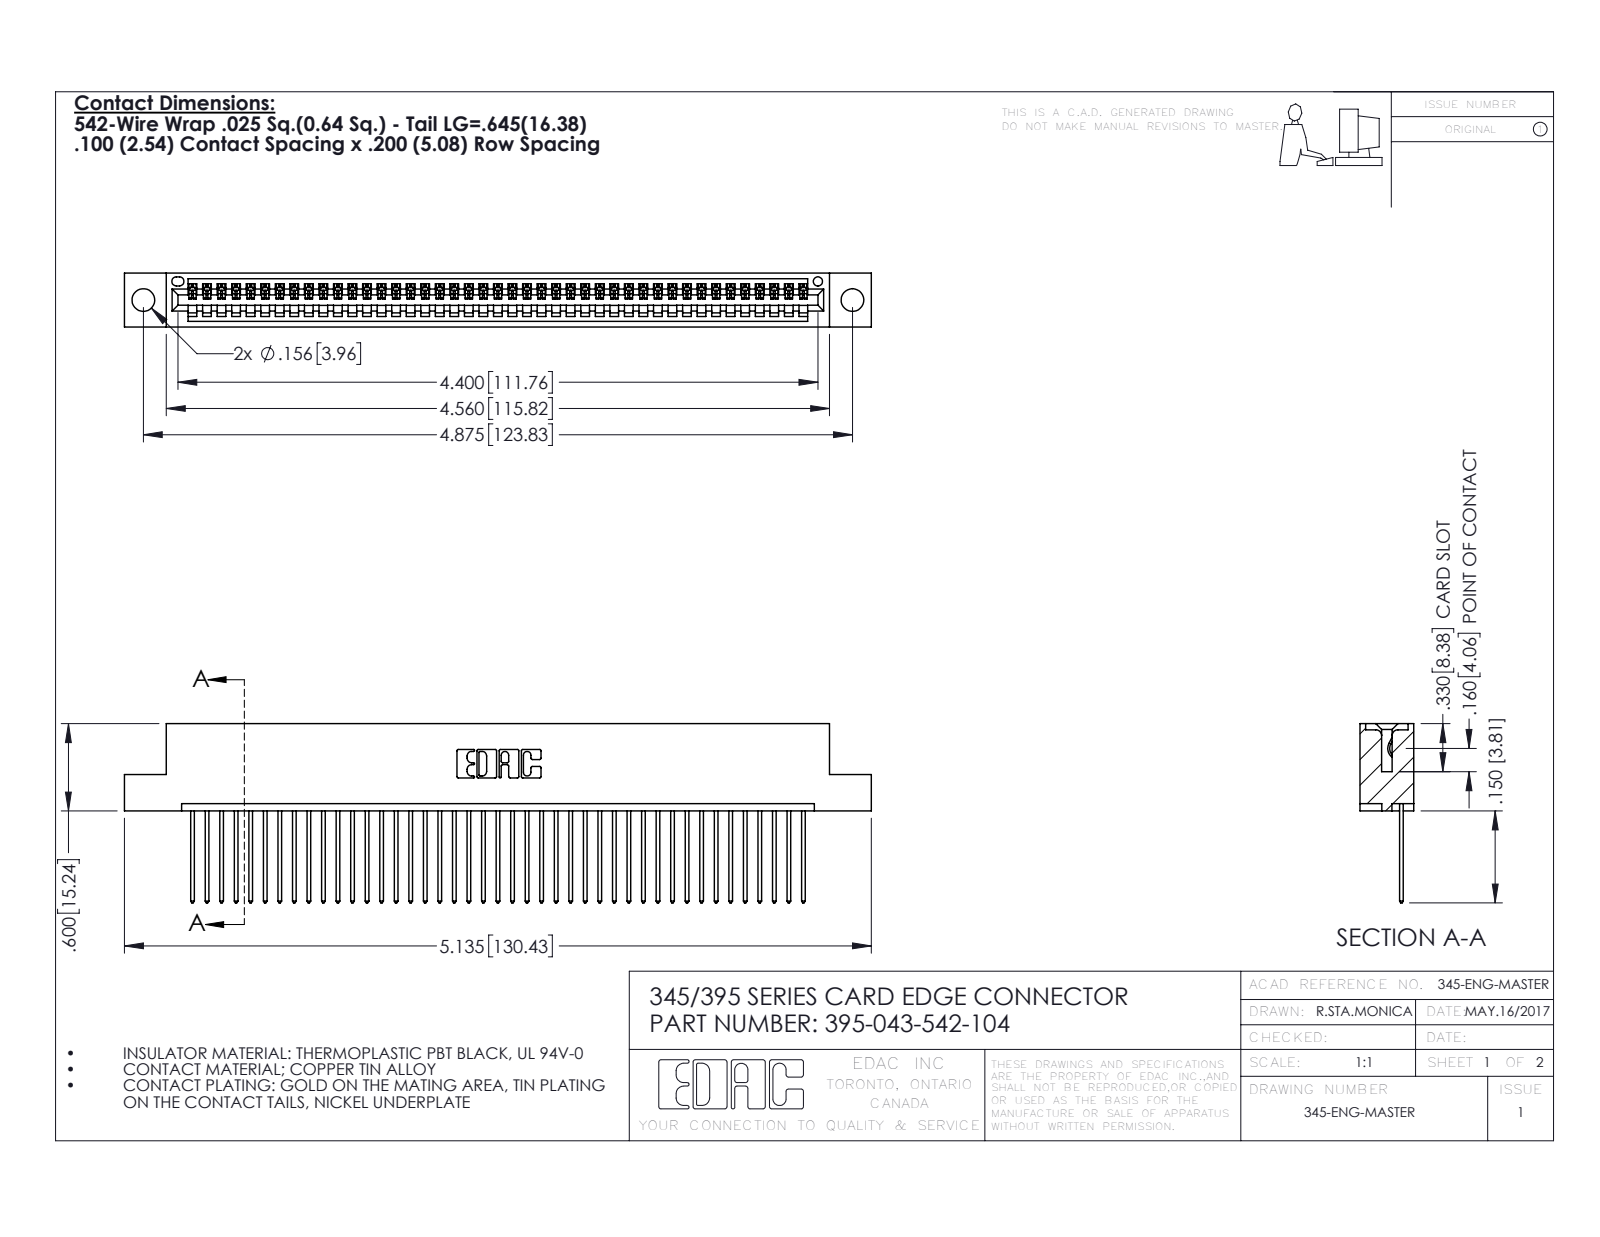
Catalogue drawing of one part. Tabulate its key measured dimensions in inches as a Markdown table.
| quantity | value |
| --- | --- |
| part name | 345-292-001_345-293-142; 395-043-542-104; 345 Part_Flush Mounting Lugs - 0.156 Dia-TH |
| STEP written by | SolidWorks 2016 (CONFIG_CONTROL_DESIGN) |
| units | inches |
| bodies | 44 solids, 2620 faces (1800 planar, 820 cylindrical, 0 other) |
| overall size | 5.135 × 1.232 × 0.37 |
| volume | 0.757 in³ |
| surface area | 26.21 in² |
| round holes (diameter × count) | 0.156 × 2, 0.064 × 1 |
| partial cylindrical surfaces (radius × count) | 0.006 × 86, 0.01 × 86, 0.01 × 22, 0.007 × 6, 0.031 × 6, 0.026 × 3, 0.031 × 2, 0.04 × 2 |
| main face-to-face distances | 0.072, 0.298, 0.37, 0.098, 0.272, 0.025, 0.2, 0.225, 0.149, 0.072 |
| hole center spacings | 0.27, 4.639, 4.875 |
